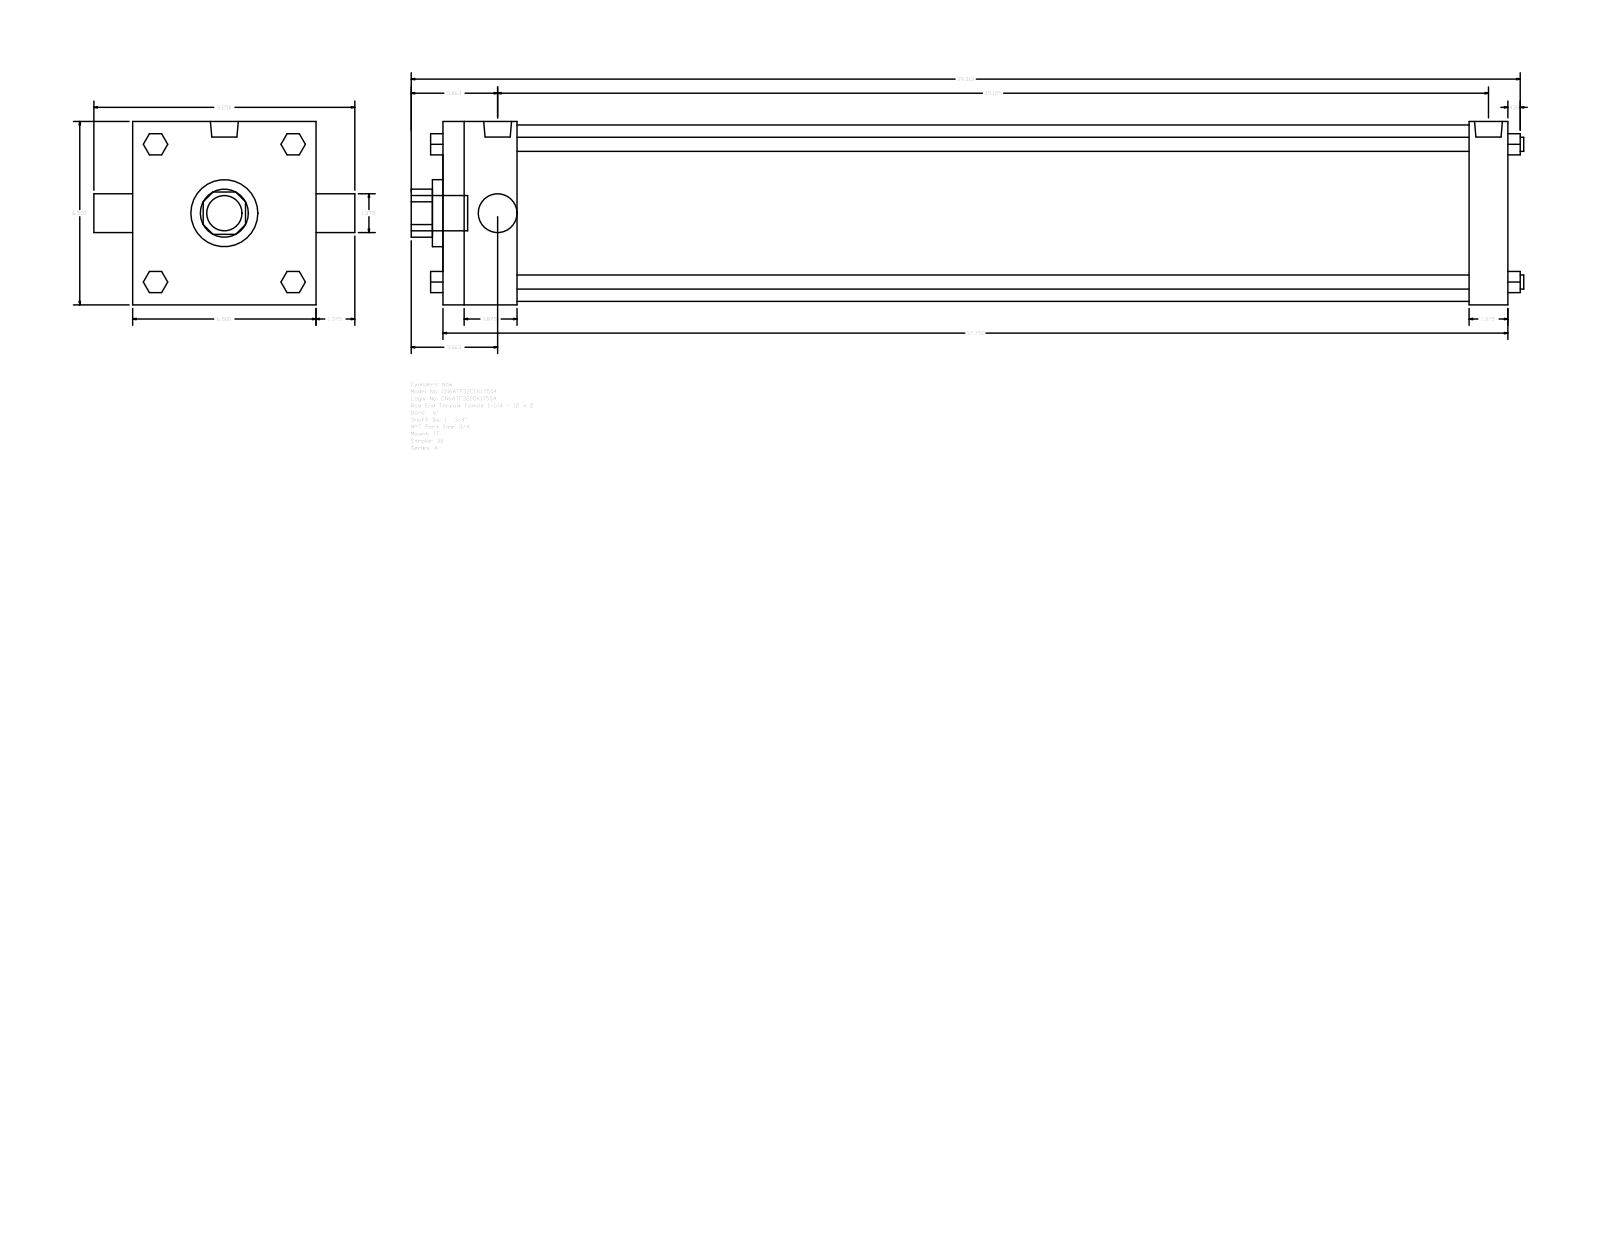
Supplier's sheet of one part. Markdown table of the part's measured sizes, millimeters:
| quantity | value |
| --- | --- |
| part name | A_TF__0600_1.75 |
| STEP written by | GSSL Pune (CONFIG_CONTROL_DESIGN) |
| units | millimeters |
| bodies | 0 solids, 120 faces (92 planar, 28 cylindrical, 0 other) |
| overall size | 1001.71 × 234.95 × 165.1 |
| round holes (diameter × count) | 34.92 × 1, 44.45 × 1, 60.33 × 1, 158.75 × 1 |
| round bosses / shafts (diameter × count) | 12.7 × 4, 15.08 × 3, 25.12 × 2, 31.75 × 1 |
| partial cylindrical surfaces (radius × count) | 21.63 × 1 |
| main face-to-face distances | 165.1, 958.85, 34.92, 66.68, 892.17, 923.93, 857.25, 19.05, 61.97, 107.34 |
